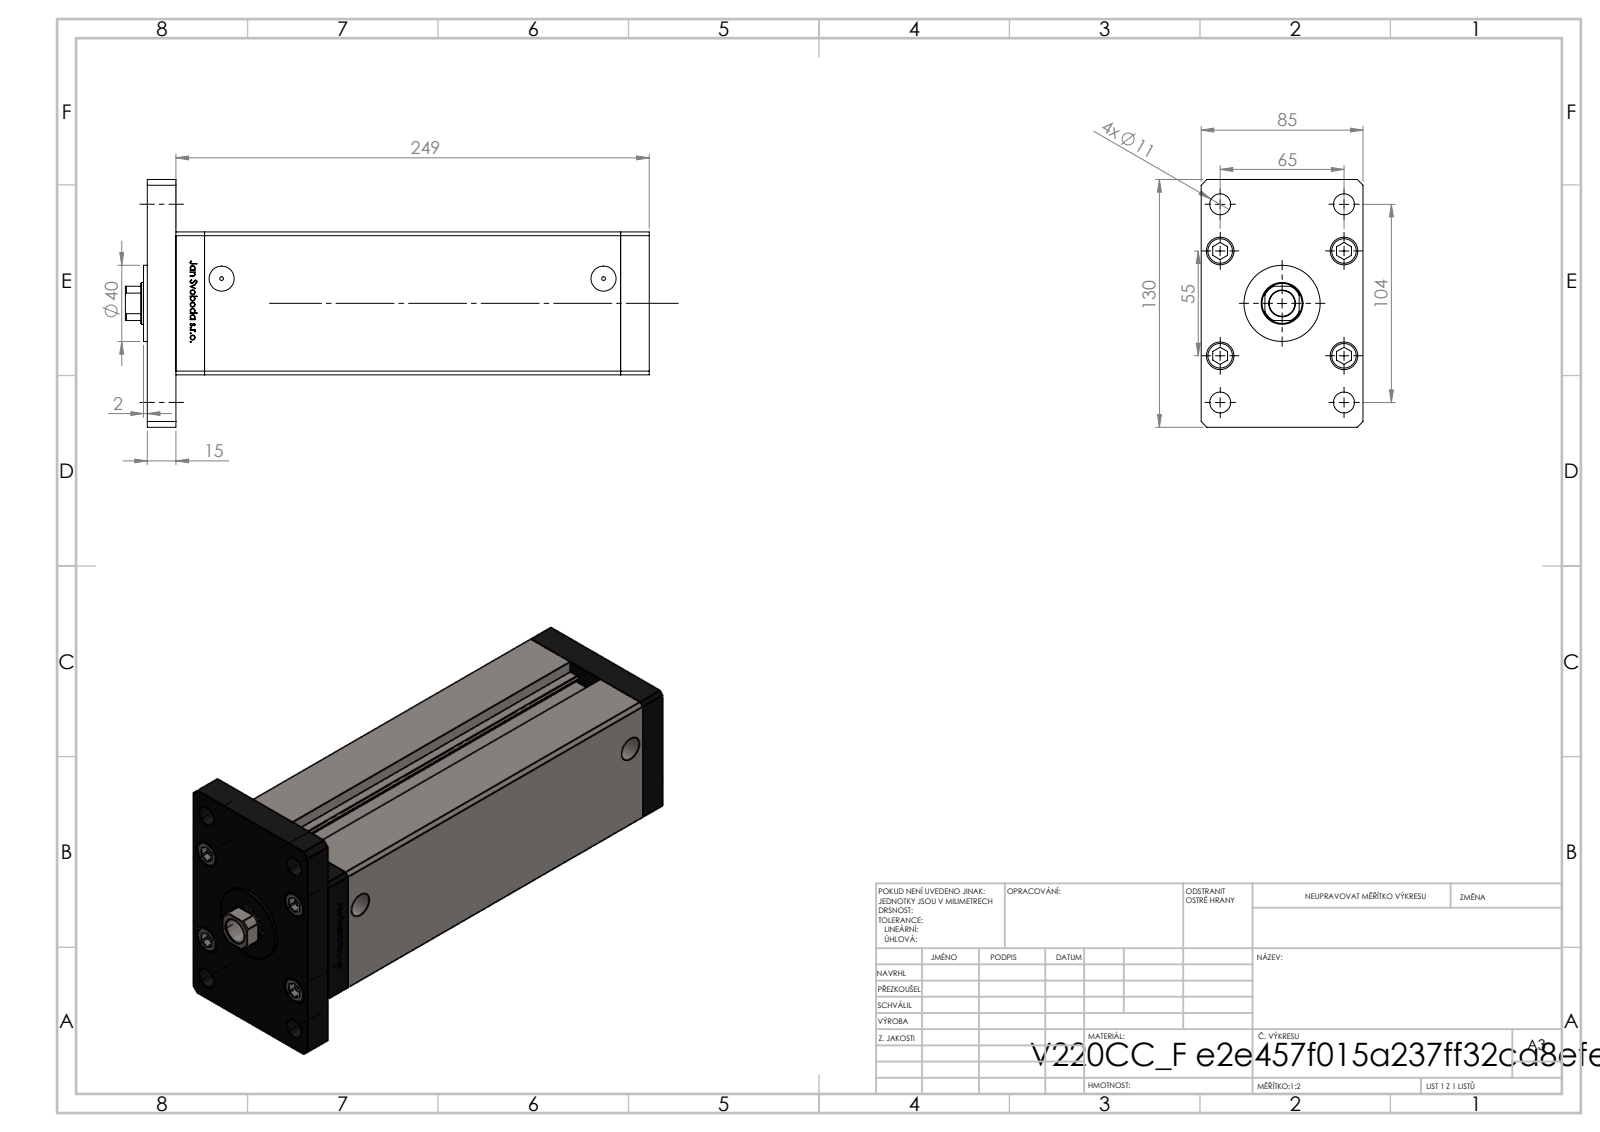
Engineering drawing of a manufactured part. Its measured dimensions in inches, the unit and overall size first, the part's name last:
Units: inches
Overall size (bounding box): 10.827 × 5.118 × 3.346
Round holes (diameter × count): ⌀0.433 ×9, ⌀0.61 ×5, ⌀0.394 ×4, ⌀0.571 ×4, ⌀0.079 ×2, ⌀0.518 ×2, ⌀0.531 ×1, ⌀0.866 ×1, ⌀0.925 ×1
Round bosses / shafts (diameter × count): ⌀0.315 ×9, ⌀0.571 ×5, ⌀1.575 ×1
Partial cylindrical surfaces — rounded edges, fillets, slot ends (radius × count): R0.037 ×2, R0.413 ×1
Main face-to-face distances: 0.591, 3.346, 2.953, 9.193, 9.783, 8.602, 1.181, 10.374, 0.413, 1.083
Hole centre spacings: 1.102, 0.965, 1.676, 2.414, 2.559, 2.735, 3.13, 4.043
Volume: 93.73 in³ · Surface area: 366.2 in²
Bodies: 19 solids, 1308 faces (515 planar, 187 cylindrical, 606 other)
Part name (STEP PRODUCT): V220C_F_MIDDLE; V220C_F; V220C_FRONT_F; ALLEN BOLT (+2 more)
STEP written by: SolidWorks 2019 (CONFIG_CONTROL_DESIGN)
